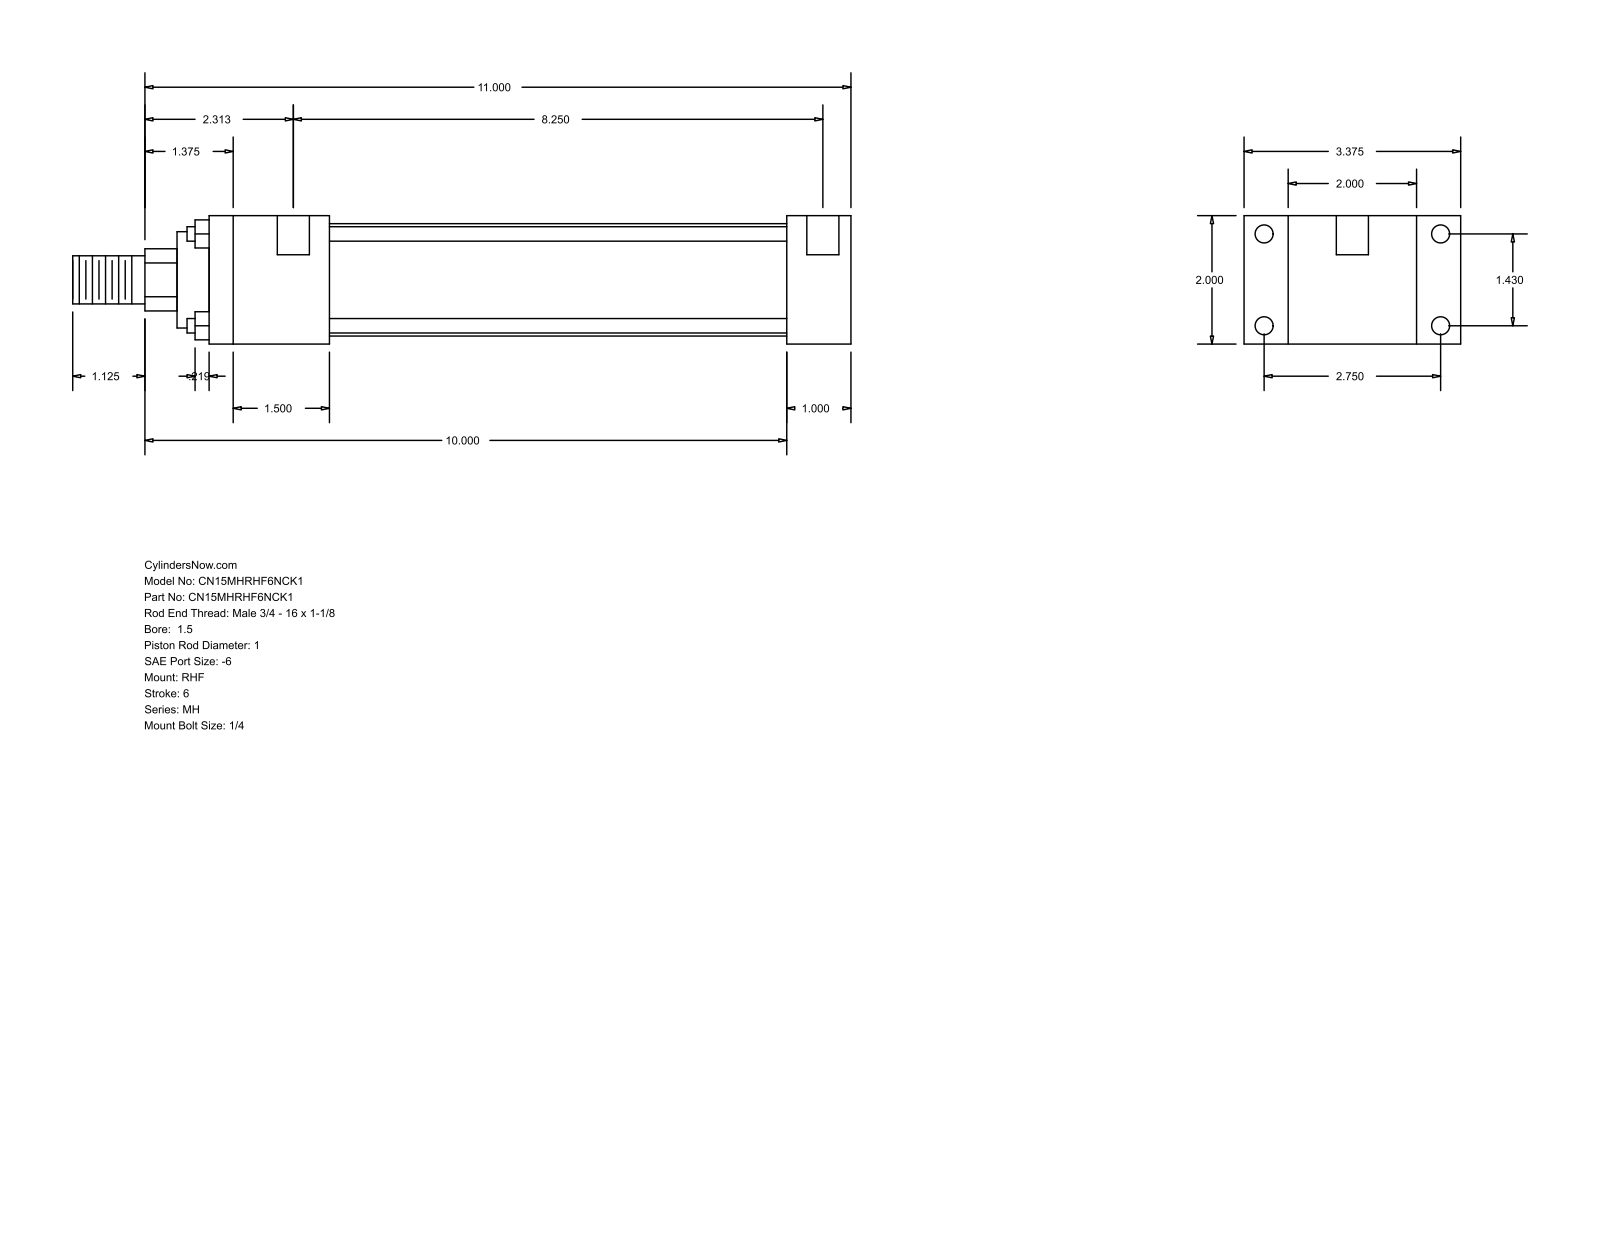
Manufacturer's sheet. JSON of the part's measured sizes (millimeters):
{"part_name": "MH_RHF__0150_1", "step_written_by": "GSSL Pune (CONFIG_CONTROL_DESIGN)", "units": "millimeters", "bodies": {"solids": 0, "faces": 88, "planar": 60, "cylindrical": 28, "other": 0}, "overall_size": [307.98, 85.72, 50.8], "round_holes": [[5.56, 4], [7.14, 4], [12.7, 2]], "round_bosses_or_shafts": [[5.71, 4], [44.45, 1], [38.1, 1], [25.4, 1], [19.05, 1]], "partial_cylinders_radius": [[12.29, 1]], "face_to_face_distances": [50.8, 25.4, 17.46, 68.26, 85.72, 254, 228.6, 47.63, 180.97, 206.37], "hole_center_spacings": [36.32, 69.84, 78.72, 212.73, 3.18, 209.55]}
